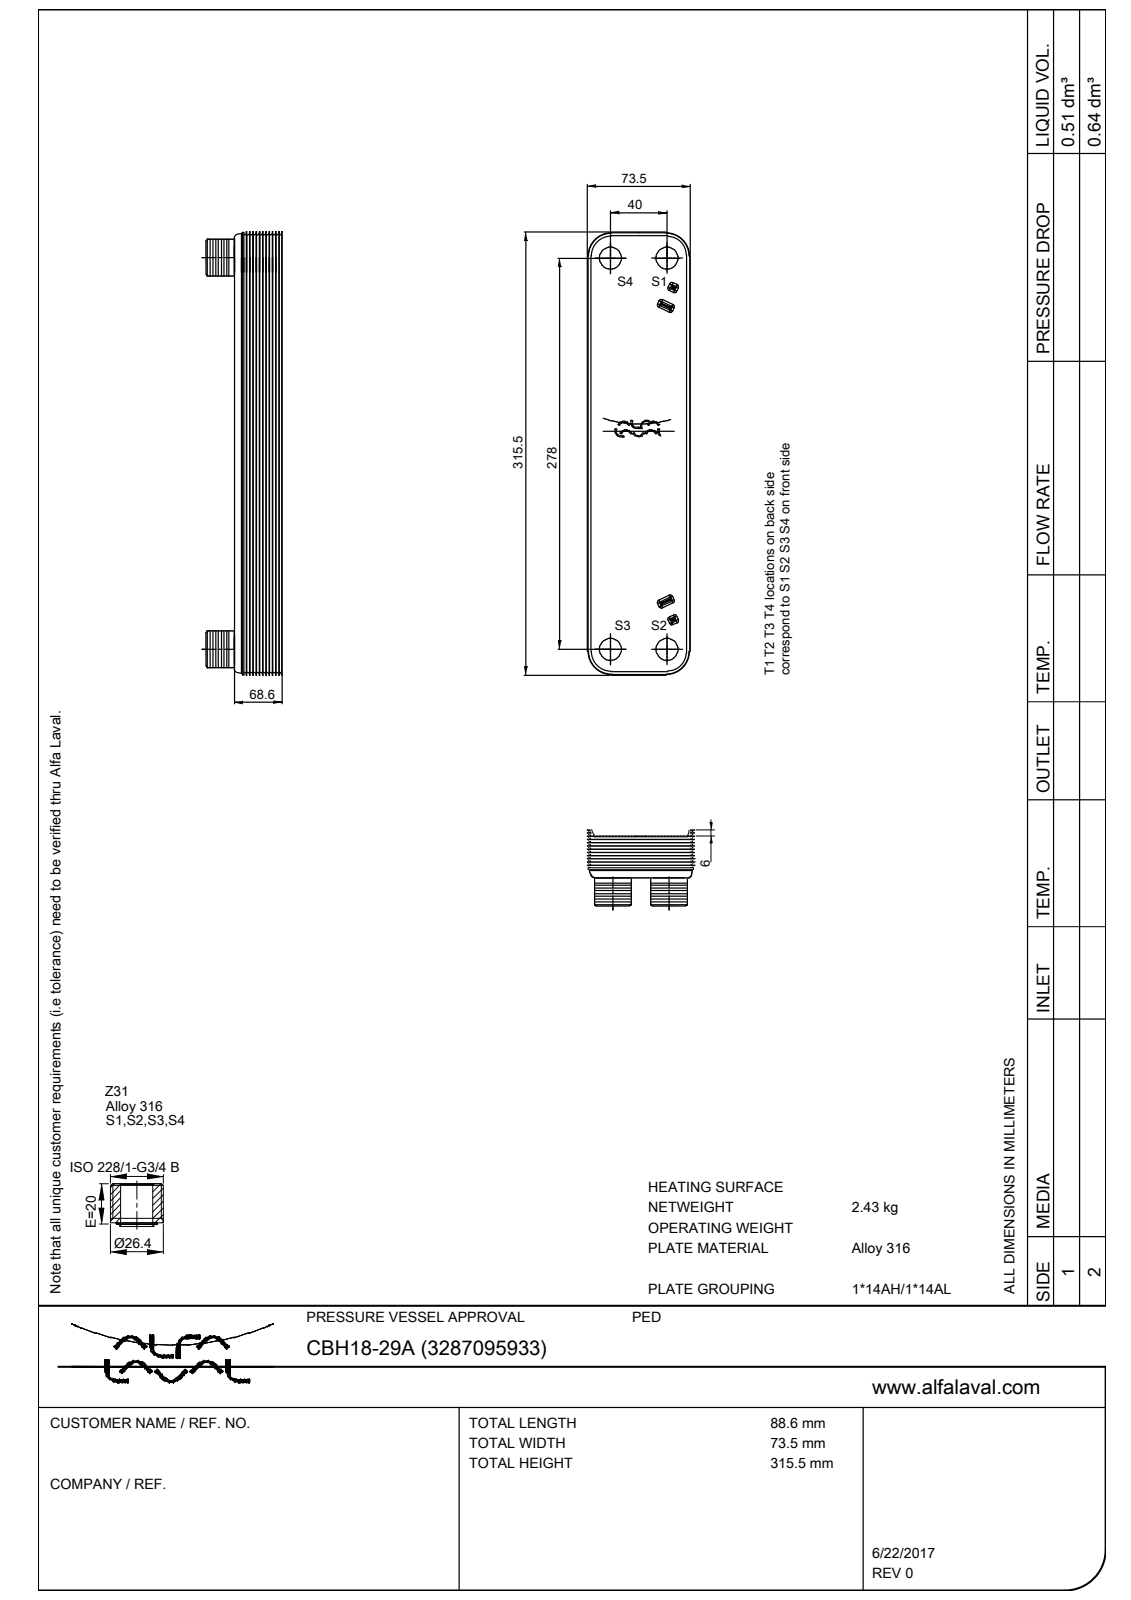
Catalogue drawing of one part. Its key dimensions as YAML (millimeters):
part_name: "CBH18_CH_29H; CBH18_FP_S1S2S3S4_16; CBH18_PP; Z31 (+1 more)"
step_written_by: "PRO/ENGINEER BY PARAMETRIC TECHNOLOGY CORPORATION, 2007390 (CONFIG_CONTROL_DESIGN)"
units: millimeters
bodies: {solids: 7, faces: 480, planar: 128, cylindrical: 144, other: 208}
overall_size: [319, 90.6, 77.5]
volume: 1552000
surface_area: 234187
round_holes:
  - {diameter: 16, count: 4}
  - {diameter: 16.75, count: 4}
  - {diameter: 20.5, count: 4}
round_bosses_or_shafts:
  - {diameter: 26.44, count: 4}
  - {diameter: 18, count: 4}
partial_cylinders:
  - {radius: 1, count: 18}
  - {radius: 0.4, count: 16}
  - {radius: 0.7, count: 16}
  - {radius: 1.4, count: 16}
  - {radius: 1.7, count: 16}
  - {radius: 0.5, count: 4}
  - {radius: 1.5, count: 4}
  - {radius: 20, count: 4}
face_to_face_distances: [1, 63.9, 62.9, 64.9, 77.5, 1.04, 1.15, 65.05, 7.74, 1.01]
hole_center_spacings: [40, 278, 280.86]
